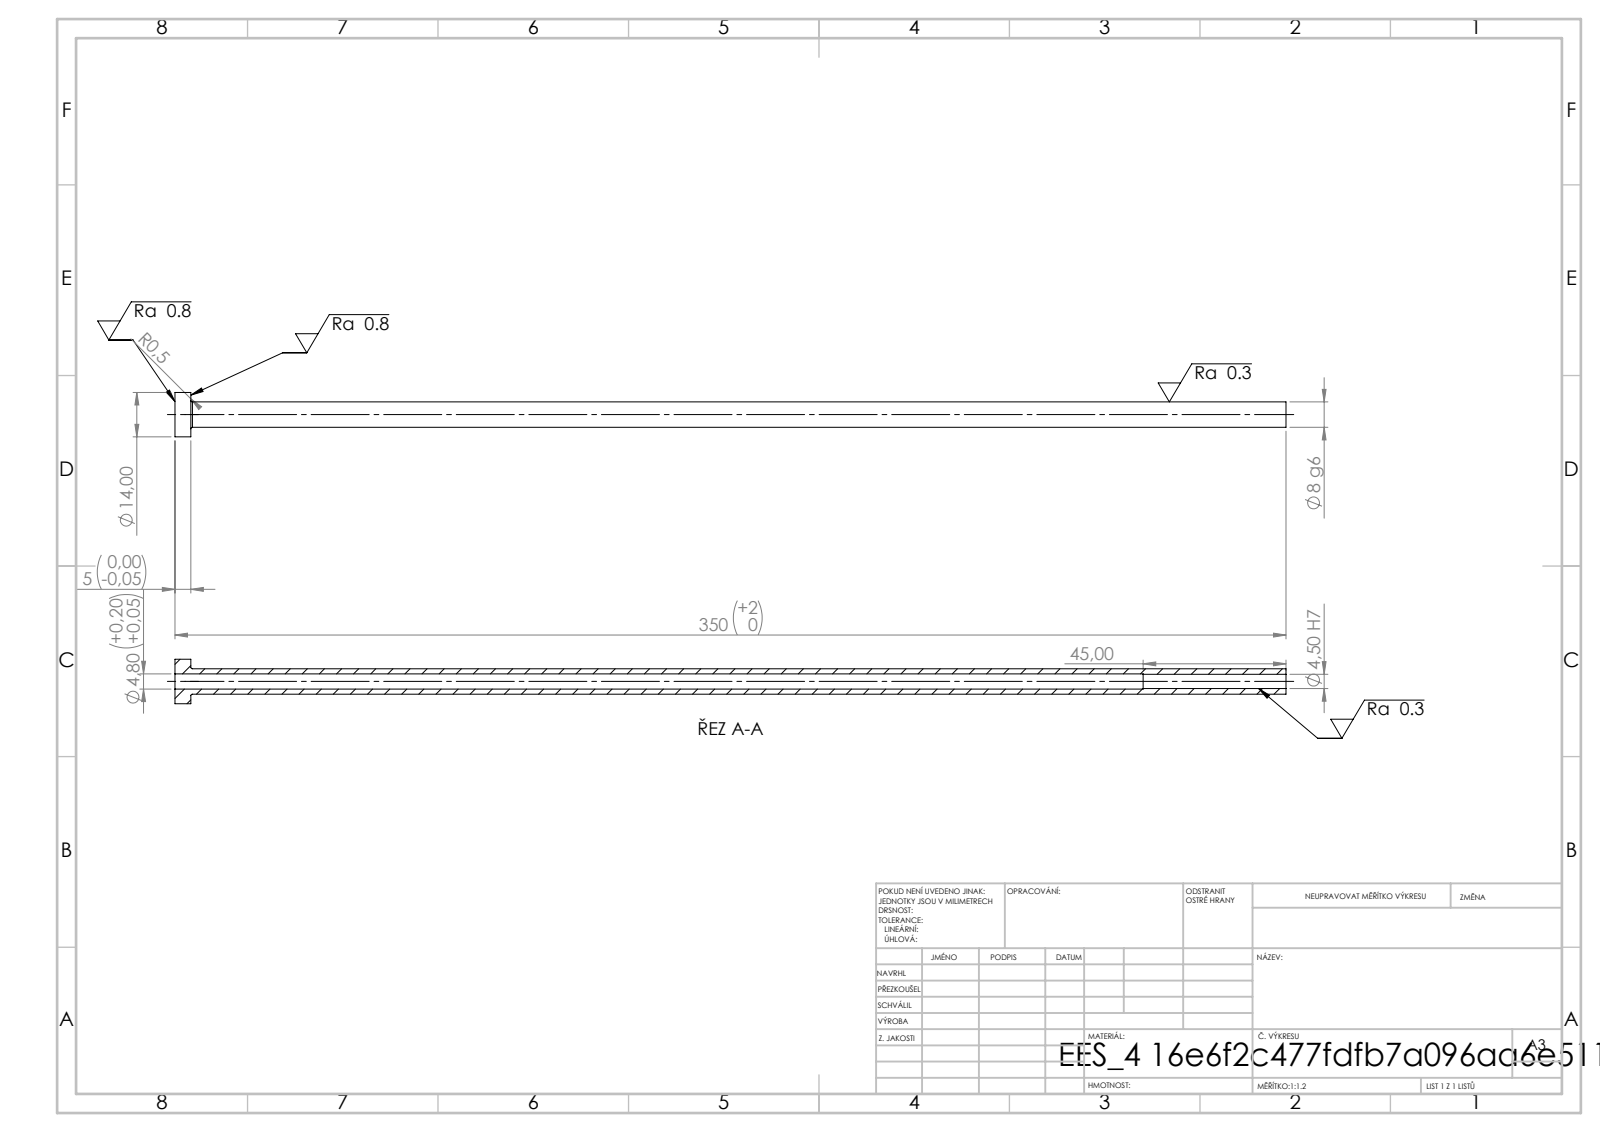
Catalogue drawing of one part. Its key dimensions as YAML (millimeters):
step_written_by: "SolidWorks 2019 (CONFIG_CONTROL_DESIGN)"
units: millimeters
bodies: {solids: 1, faces: 14, planar: 4, cylindrical: 8, other: 2}
overall_size: [350, 14, 14]
volume: 11878
surface_area: 14397
round_holes:
  - {diameter: 4.5, count: 1}
  - {diameter: 4.8, count: 1}
round_bosses_or_shafts:
  - {diameter: 14, count: 1}
  - {diameter: 8, count: 1}
face_to_face_distances: [5, 350, 345, 305, 300, 45]
